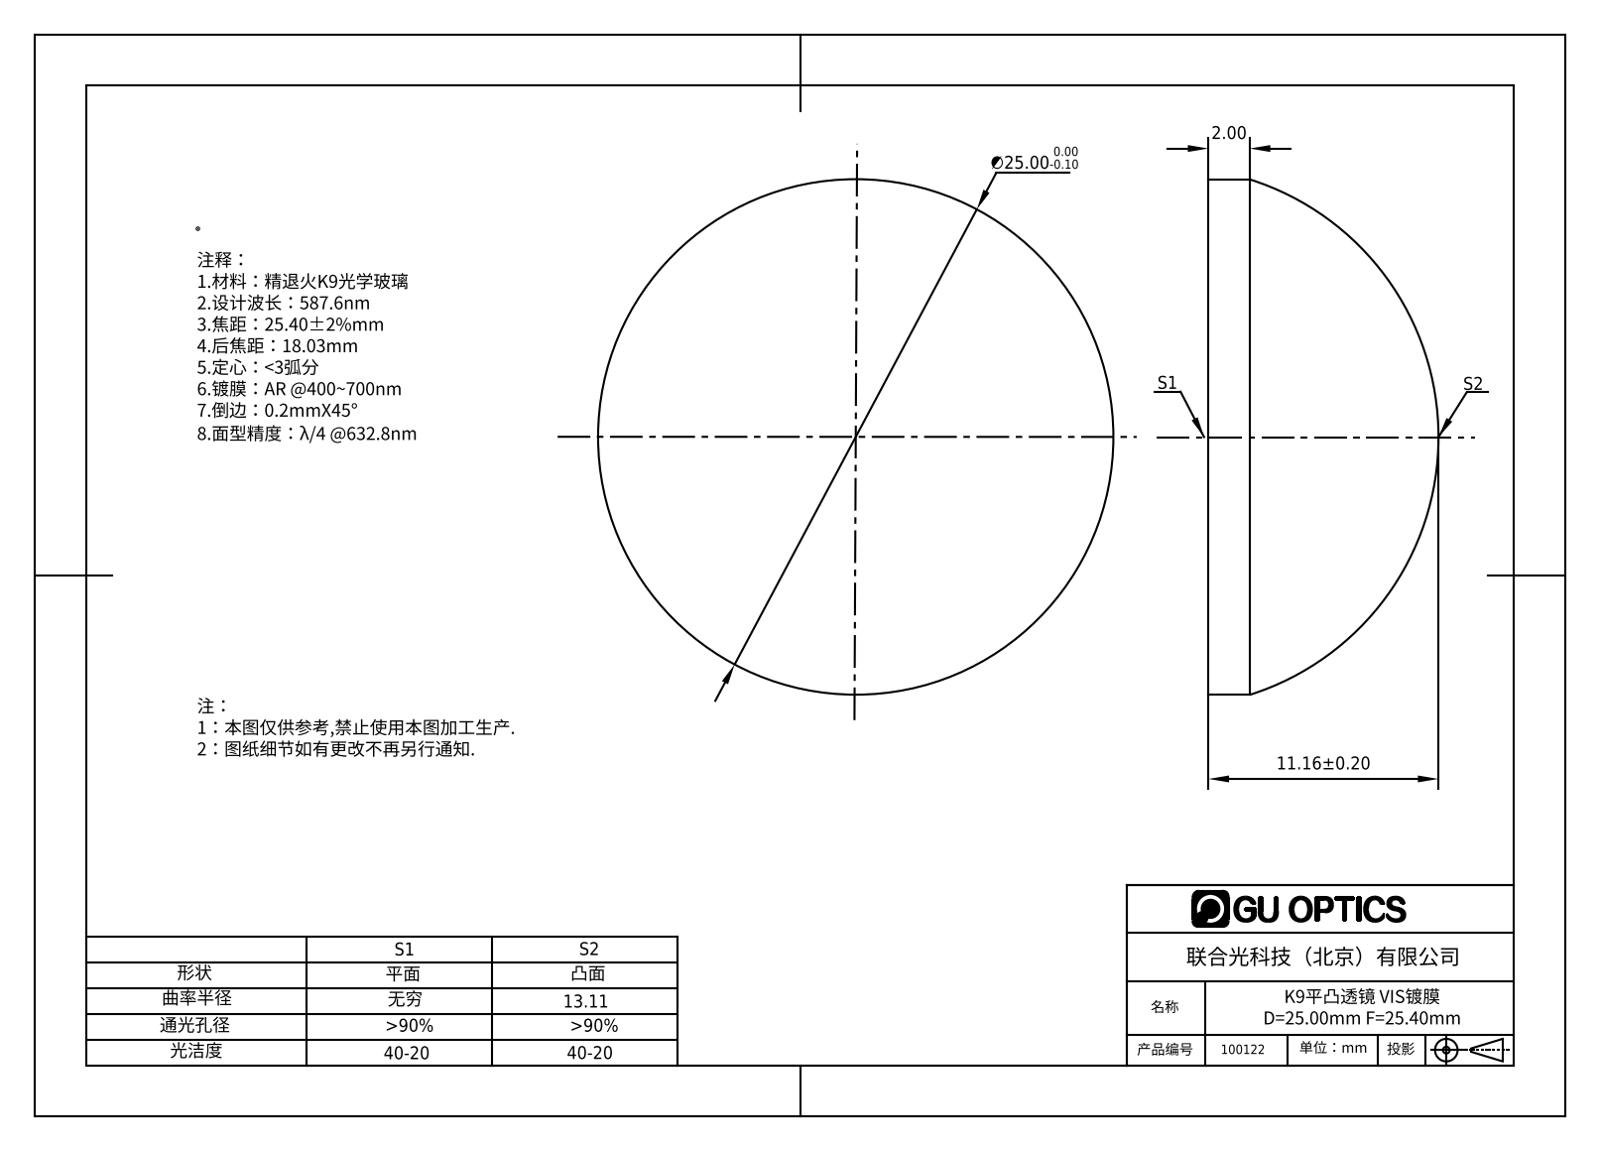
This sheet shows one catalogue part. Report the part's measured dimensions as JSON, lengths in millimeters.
{"part_name": "100122", "step_written_by": "SolidWorks 2016 (AUTOMOTIVE_DESIGN)", "units": "millimeters", "bodies": {"solids": 1, "faces": 5, "planar": 1, "cylindrical": 2, "other": 2}, "overall_size": [25, 25, 11.16], "volume_mm3": 3632, "surface_area_mm2": 1402, "round_bosses_or_shafts": [[25, 1]]}
